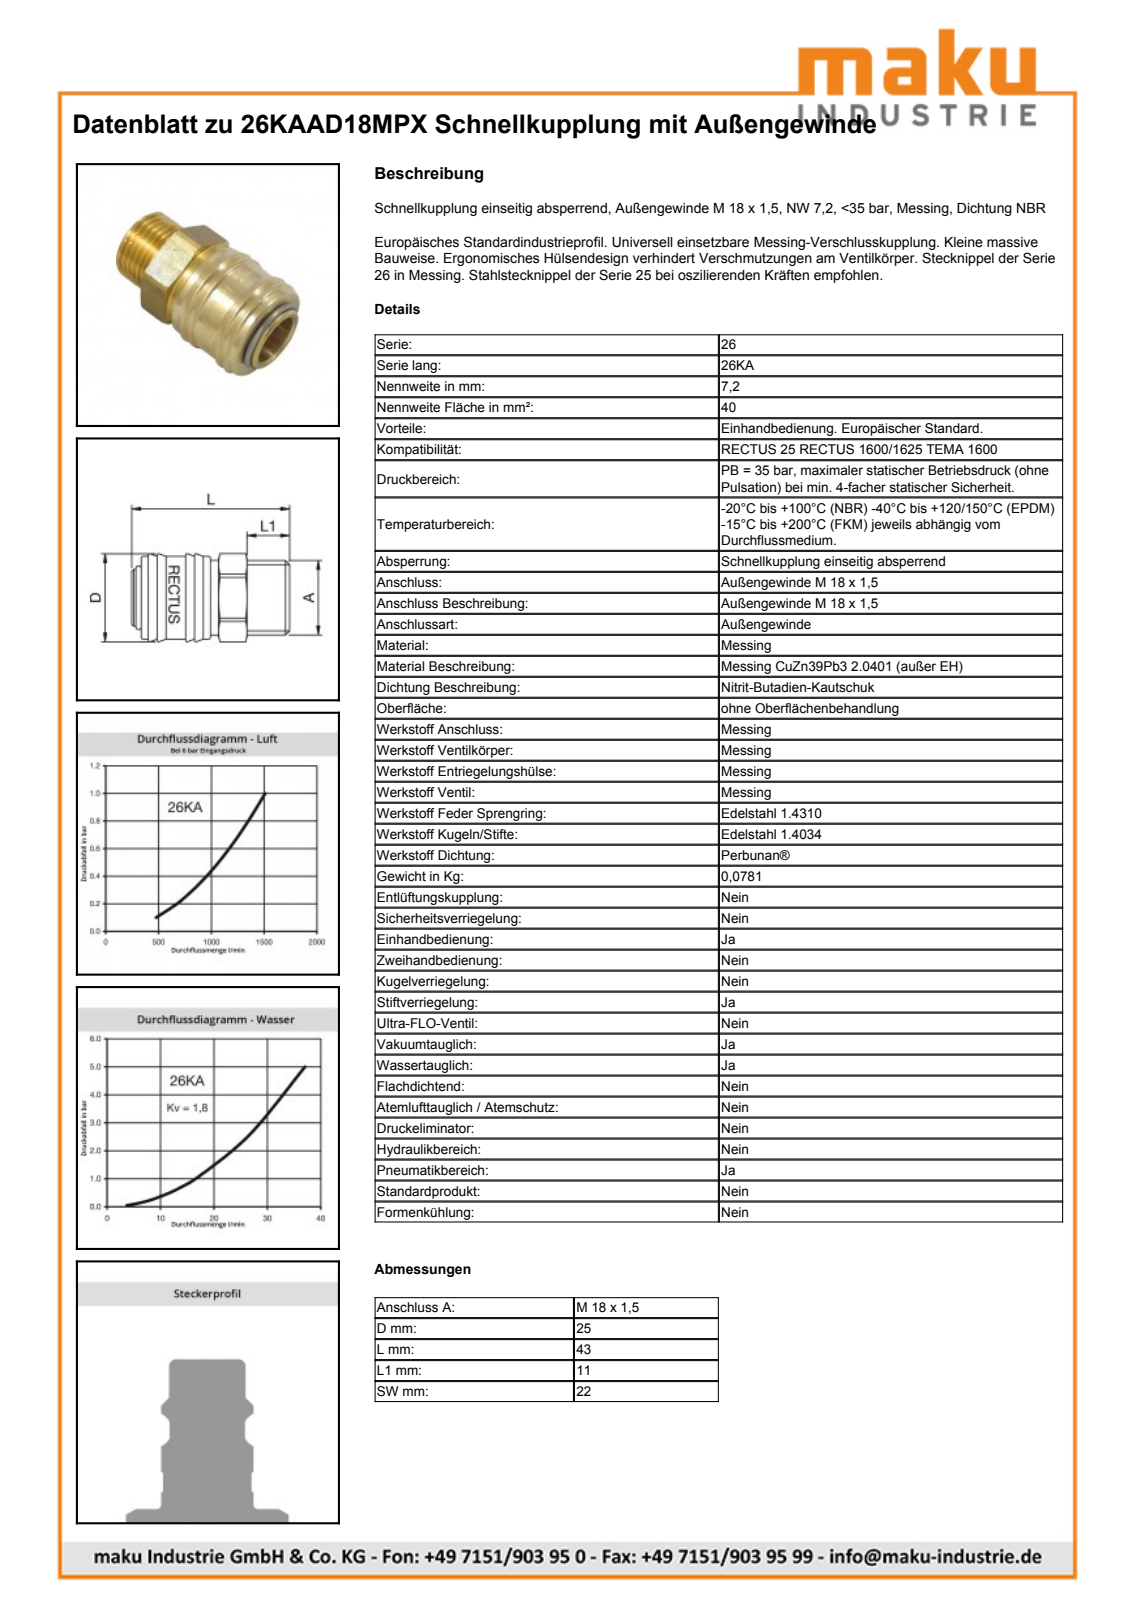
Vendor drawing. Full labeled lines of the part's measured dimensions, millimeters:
Part name (STEP PRODUCT): 26KAAD18MPX; 26KAAD18MPX_PART2; 26KAAD18MPX_PART1
STEP written by: PARTsolutions (AUTOMOTIVE_DESIGN)
Units: millimetres
Bodies: 2 solids, 679 faces (236 planar, 63 cylindrical, 380 other)
Overall size (bounding box): 43 × 24.8 × 24.45
Volume: 14 769 mm³ · Surface area: 4 547 mm²
Round bosses / shafts (diameter × count): ⌀23.3 ×1, ⌀22.95 ×1, ⌀21.19 ×1, ⌀17.97 ×1, ⌀15.95 ×1, ⌀14.95 ×1
Partial cylindrical surfaces — rounded edges, fillets, slot ends (radius × count): R11.28 ×1, R12.4 ×1
Main face-to-face distances: 22, 28.5, 5.35, 33.85, 3, 31.5, 36.85, 8, 13.35, 11
